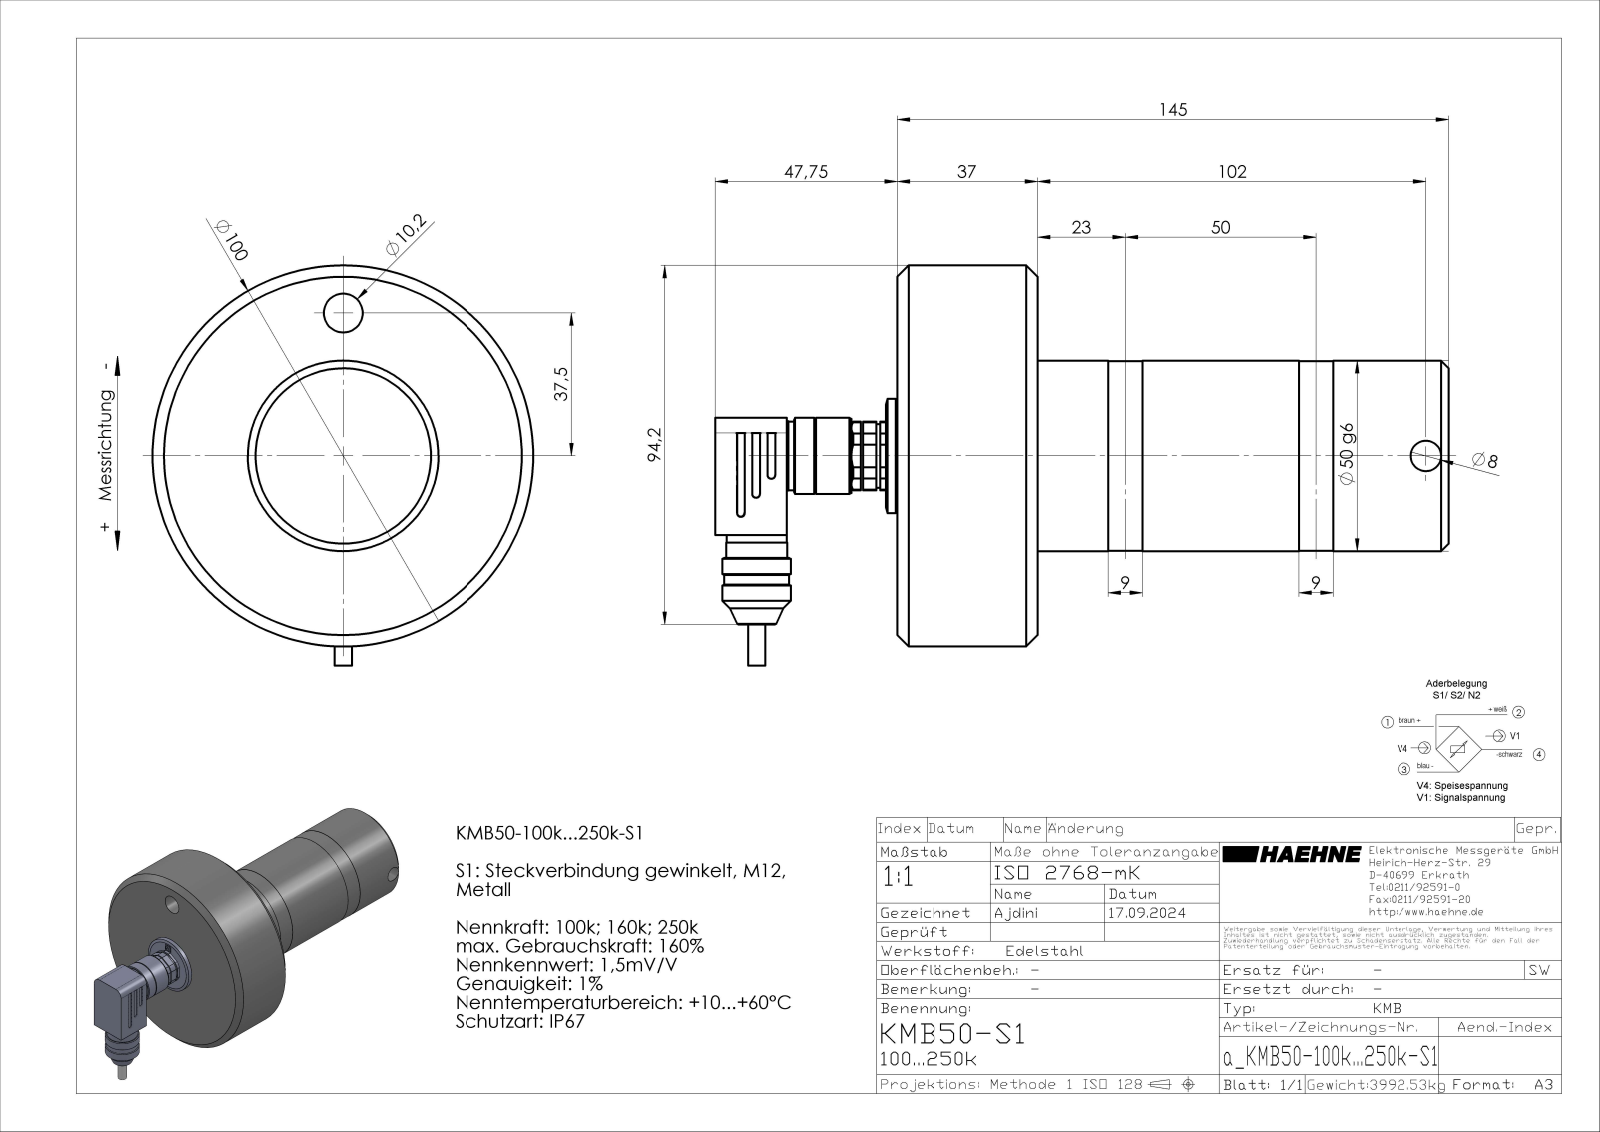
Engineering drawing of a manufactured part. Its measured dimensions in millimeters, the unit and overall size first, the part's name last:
Units: millimetres
Overall size (bounding box): 192.75 × 104.98 × 100
Round holes (diameter × count): ⌀1.22 ×5, ⌀8 ×1, ⌀10.2 ×1, ⌀14.16 ×1, ⌀15.75 ×1, ⌀16 ×1, ⌀17 ×1, ⌀18 ×1, ⌀23.5 ×1
Round bosses / shafts (diameter × count): ⌀1.5 ×4, ⌀100 ×1, ⌀50 ×1, ⌀49.8 ×1, ⌀30 ×1, ⌀25 ×1, ⌀23.16 ×1, ⌀20 ×1
Partial cylindrical surfaces — rounded edges, fillets, slot ends (radius × count): R0.2 ×12, R1 ×3, R4 ×2
Main face-to-face distances: 37, 108, 145, 192.75, 84.75, 47.75, 20, 40, 148, 3
Hole centre spacings: 1.29, 2.09, 11.14, 27.65, 1.3, 2.1, 9.88, 9.89
Volume: 491 062 mm³ · Surface area: 56 055 mm²
Bodies: 2 solids, 208 faces (92 planar, 79 cylindrical, 37 other)
Part name (STEP PRODUCT): a_KMB50-100k...250k-S1; a_KMB50-100k...150k-S1_Angebot; X02045Z1 SKINDICHT MR-M 25x1,5 _ 16x1,5 Art_ Nr_ 52104313; Option S1 ohne Kästchen
STEP written by: SolidWorks 2023 (CONFIG_CONTROL_DESIGN)
